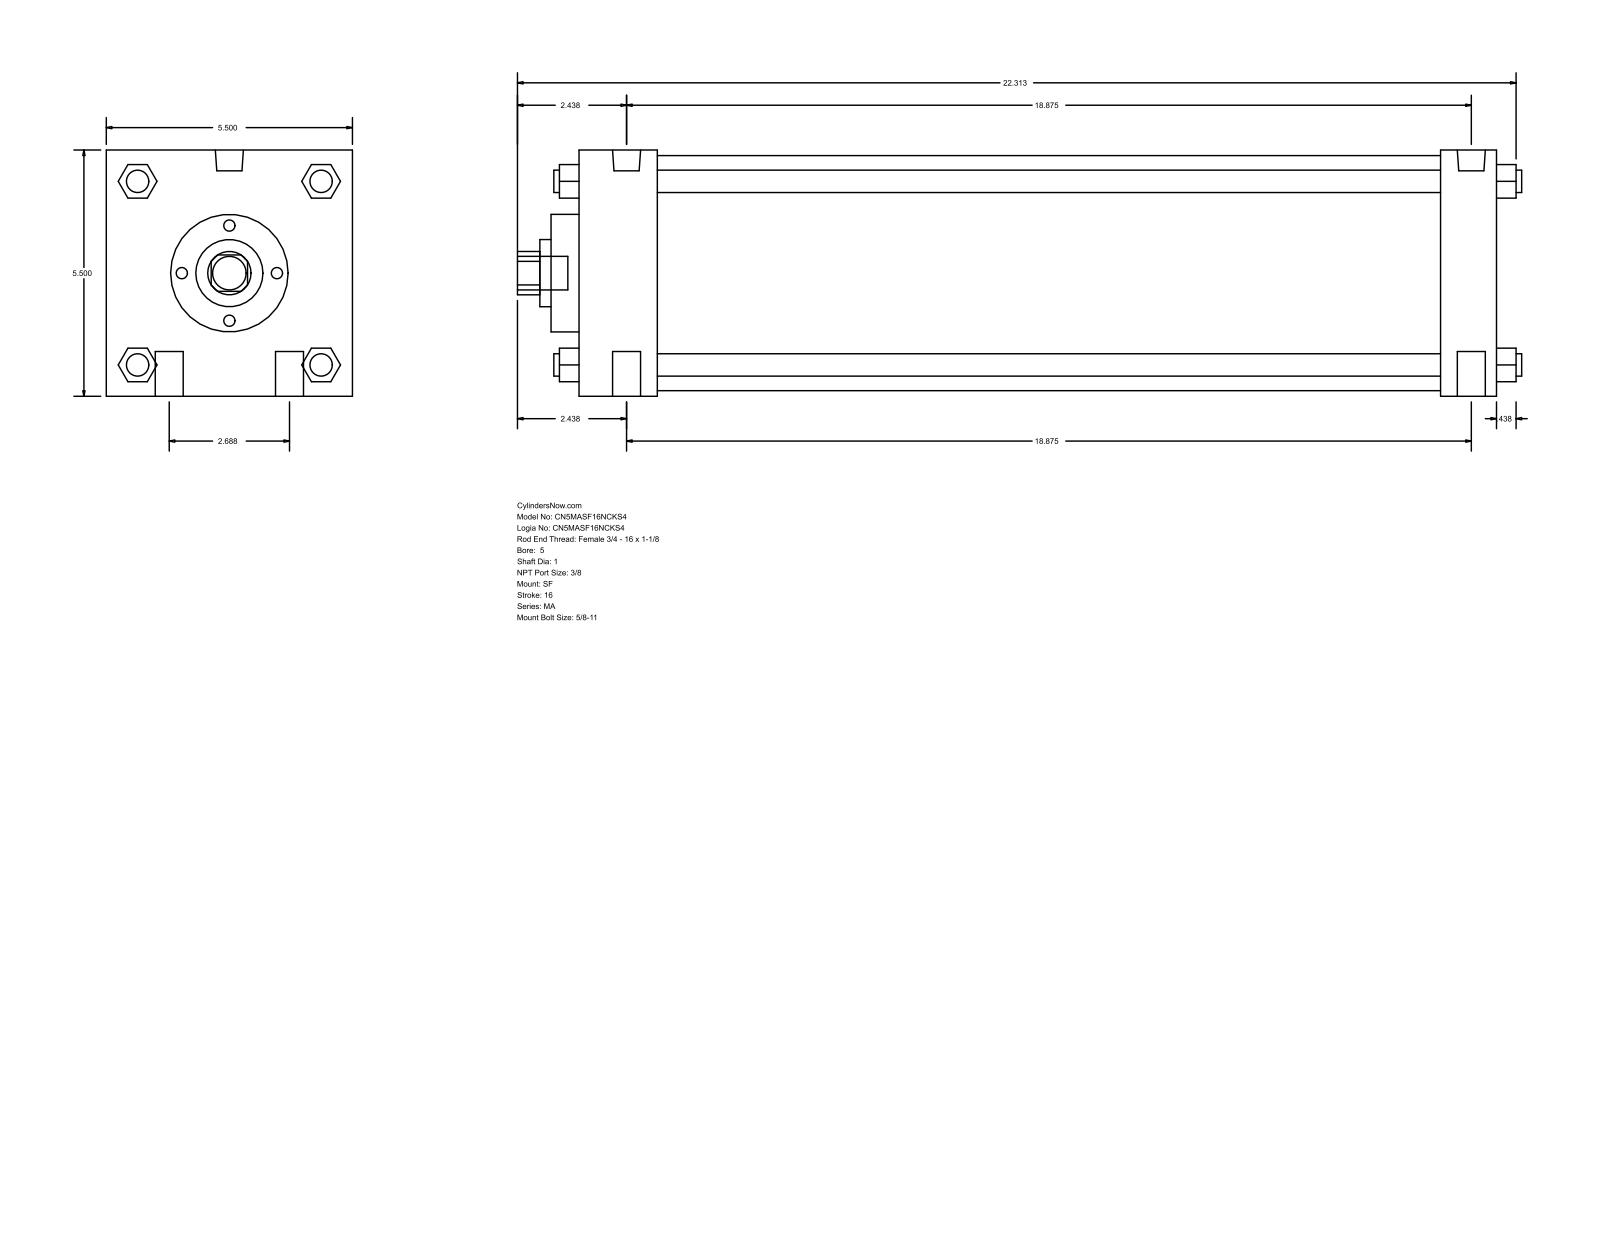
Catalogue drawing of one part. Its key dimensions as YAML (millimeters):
part_name: "MA_SF__0500_1"
step_written_by: "GSSL Pune (CONFIG_CONTROL_DESIGN)"
units: millimeters
bodies: {solids: 0, faces: 126, planar: 95, cylindrical: 31, other: 0}
overall_size: [569.91, 139.7, 139.7]
round_holes:
  - {diameter: 25.4, count: 1}
  - {diameter: 38.1, count: 1}
  - {diameter: 66.67, count: 1}
  - {diameter: 133.35, count: 1}
round_bosses_or_shafts:
  - {diameter: 15.88, count: 4}
  - {diameter: 12.7, count: 4}
  - {diameter: 15.93, count: 2}
  - {diameter: 11.11, count: 2}
  - {diameter: 19.05, count: 1}
partial_cylinders:
  - {radius: 12.29, count: 1}
face_to_face_distances: [139.7, 520.7, 44.46, 488.96, 444.5, 476.24, 31.74, 15.87, 60.33, 504.83]
